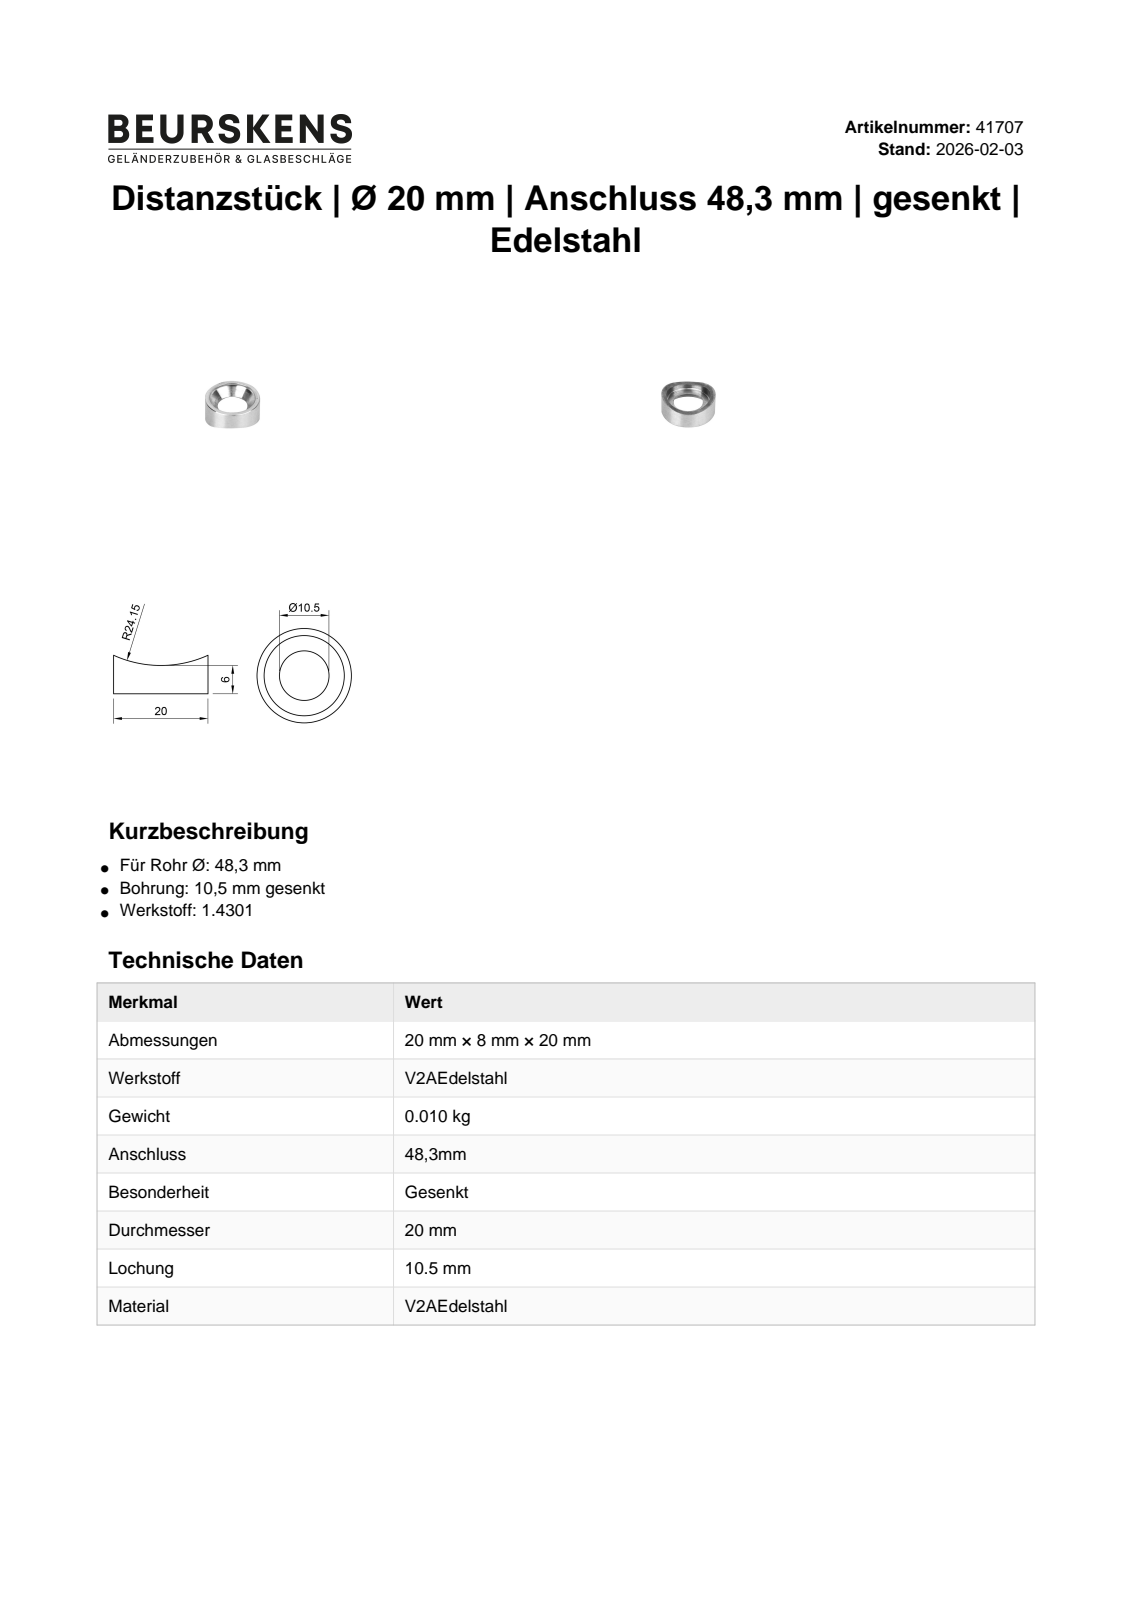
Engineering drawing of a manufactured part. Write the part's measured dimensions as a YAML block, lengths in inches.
part_name: "41707"
step_written_by: "Autodesk Inventor 2022 (AUTOMOTIVE_DESIGN)"
units: inches
bodies: {solids: 1, faces: 7, planar: 2, cylindrical: 4, other: 1}
overall_size: [0.787, 0.787, 0.322]
volume: 0.064
surface_area: 1.696
round_holes:
  - {diameter: 0.413, count: 1}
  - {diameter: 0.669, count: 1}
round_bosses_or_shafts:
  - {diameter: 0.787, count: 1}
partial_cylinders:
  - {radius: 0.951, count: 1}
face_to_face_distances: [0.219]
